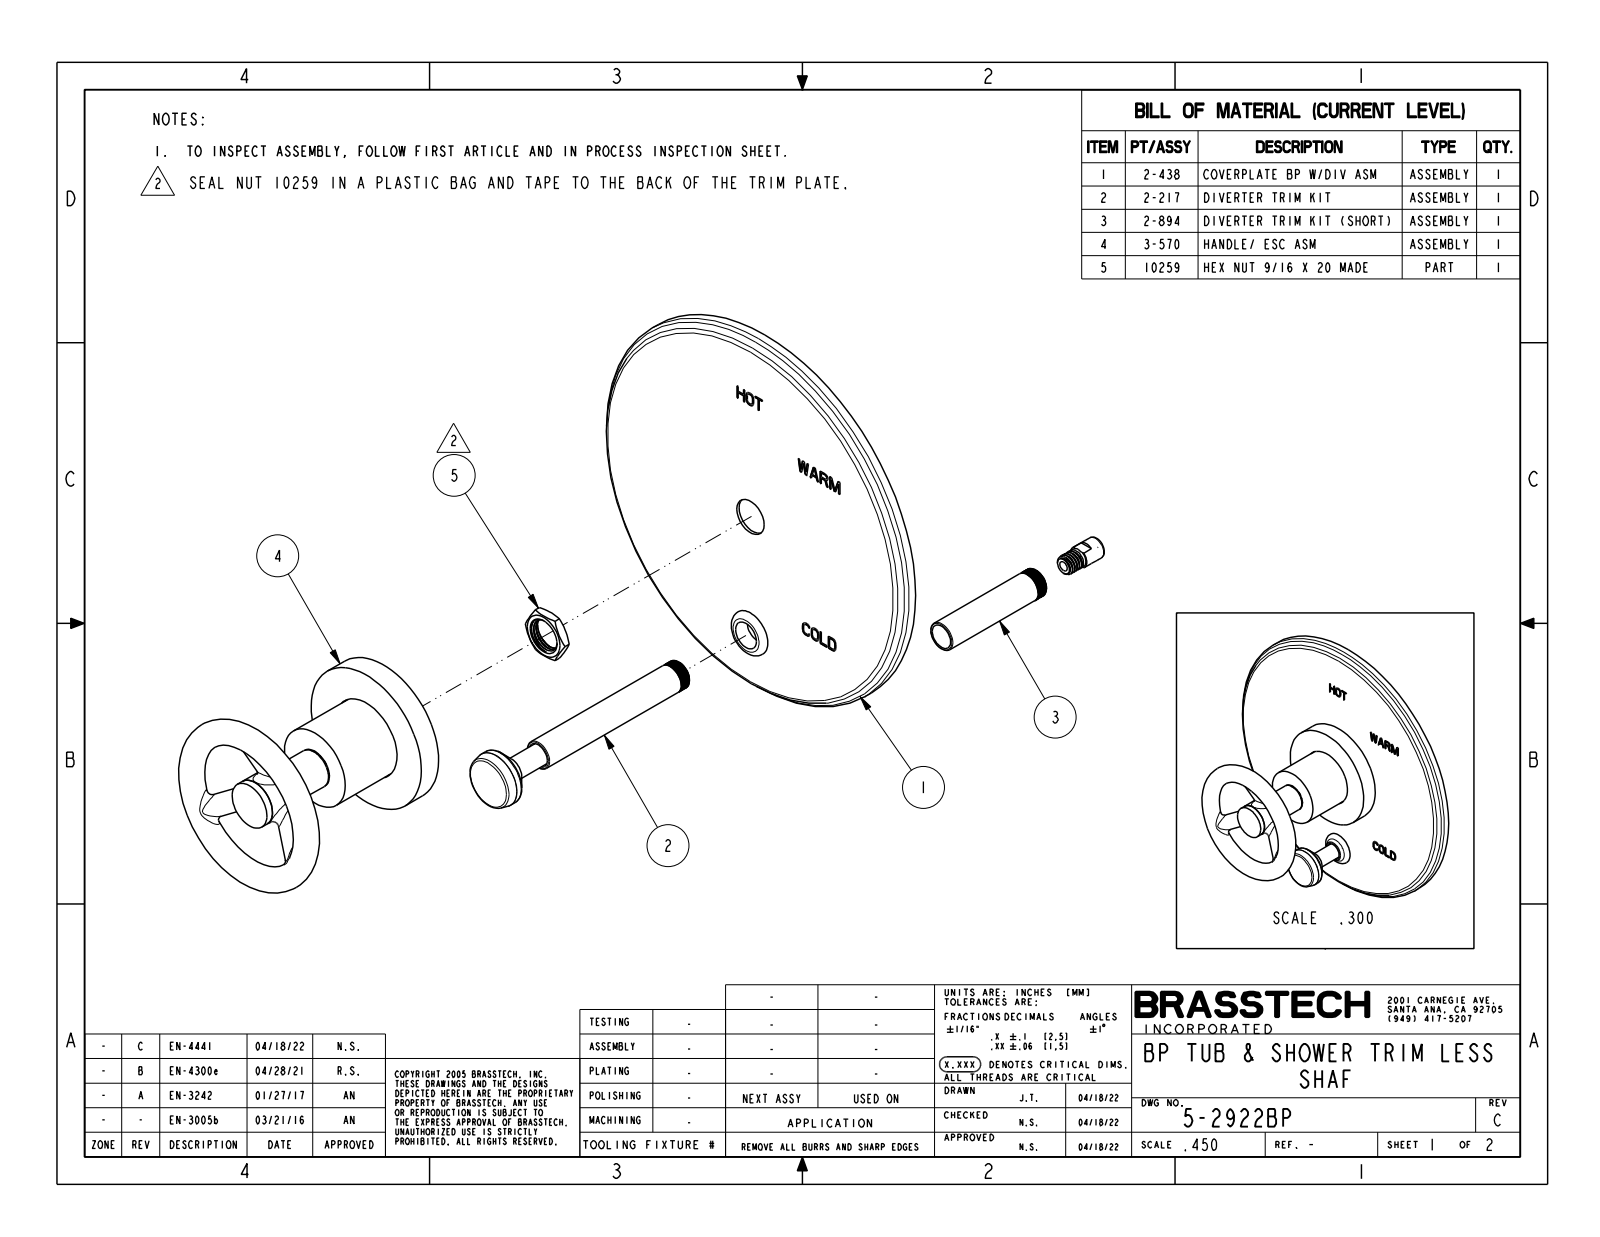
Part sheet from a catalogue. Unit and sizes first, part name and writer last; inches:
Units: inches
Overall size (bounding box): 6.5 × 6.5 × 3.416
Round bosses / shafts (diameter × count): ⌀0.35 ×3, ⌀6.5 ×1, ⌀2.375 ×1, ⌀1.313 ×1, ⌀0.9 ×1, ⌀0.75 ×1, ⌀0.63 ×1, ⌀0.472 ×1
Main face-to-face distances: 0.313, 0.688, 0.375, 1.796, 1.483, 1.108, 1.565, 1.252, 0.877, 0.231
Volume: 15.42 in³ · Surface area: 96.67 in²
Bodies: 1 solid, 336 faces (270 planar, 24 cylindrical, 42 other)
Part name (STEP PRODUCT): 5-2922BP
STEP written by: CREO PARAMETRIC BY PTC INC, 2018400 (CONFIG_CONTROL_DESIGN)
